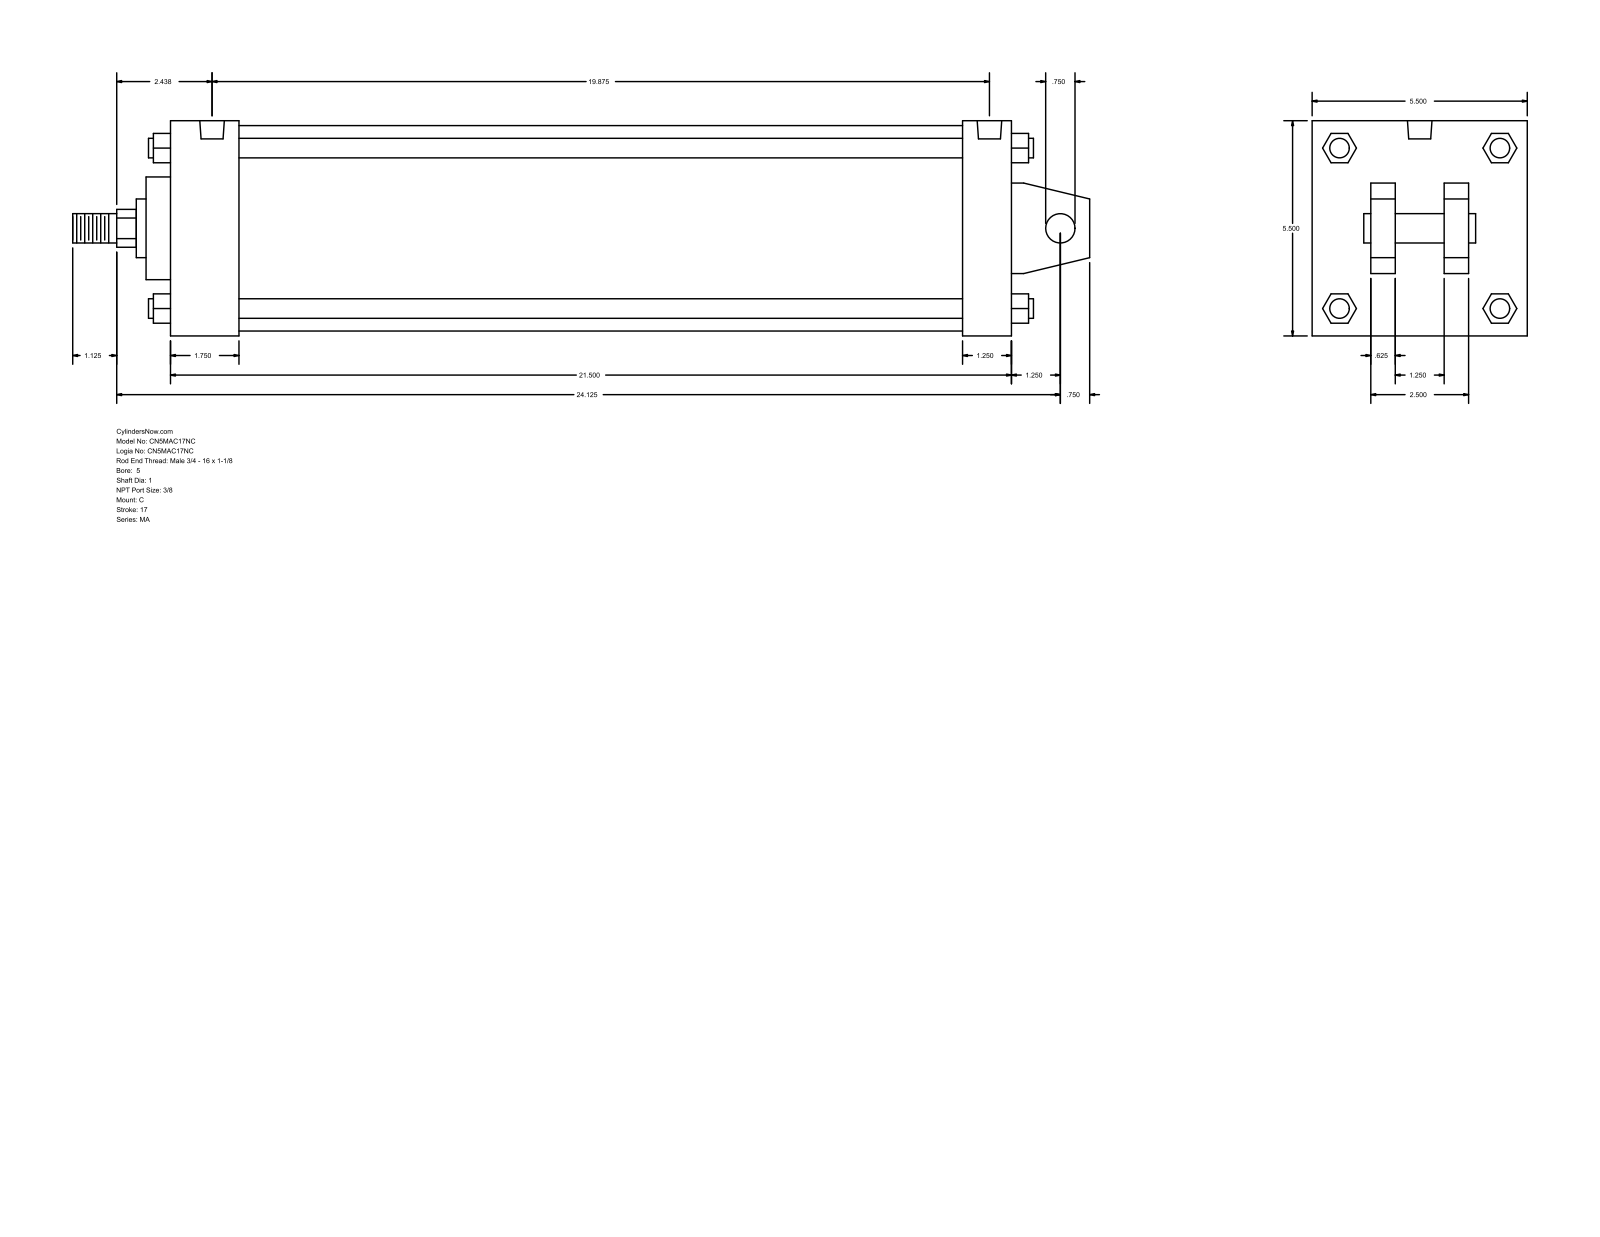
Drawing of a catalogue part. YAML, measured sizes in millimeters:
part_name: "MA_C__0500_1"
step_written_by: "GSSL Pune (CONFIG_CONTROL_DESIGN)"
units: millimeters
bodies: {solids: 0, faces: 141, planar: 109, cylindrical: 32, other: 0}
overall_size: [660.4, 139.7, 139.7]
round_holes:
  - {diameter: 11.11, count: 4}
  - {diameter: 15.93, count: 2}
round_bosses_or_shafts:
  - {diameter: 12.7, count: 4}
  - {diameter: 19.05, count: 2}
  - {diameter: 133.35, count: 1}
  - {diameter: 66.67, count: 1}
  - {diameter: 38.1, count: 1}
  - {diameter: 25.4, count: 1}
partial_cylinders:
  - {radius: 12.29, count: 1}
face_to_face_distances: [139.7, 546.1, 15.87, 514.35, 31.75, 44.46, 469.89, 501.64, 38.1, 101.6]
hole_center_spacings: [4.76, 495.31, 500.07, 504.83]
